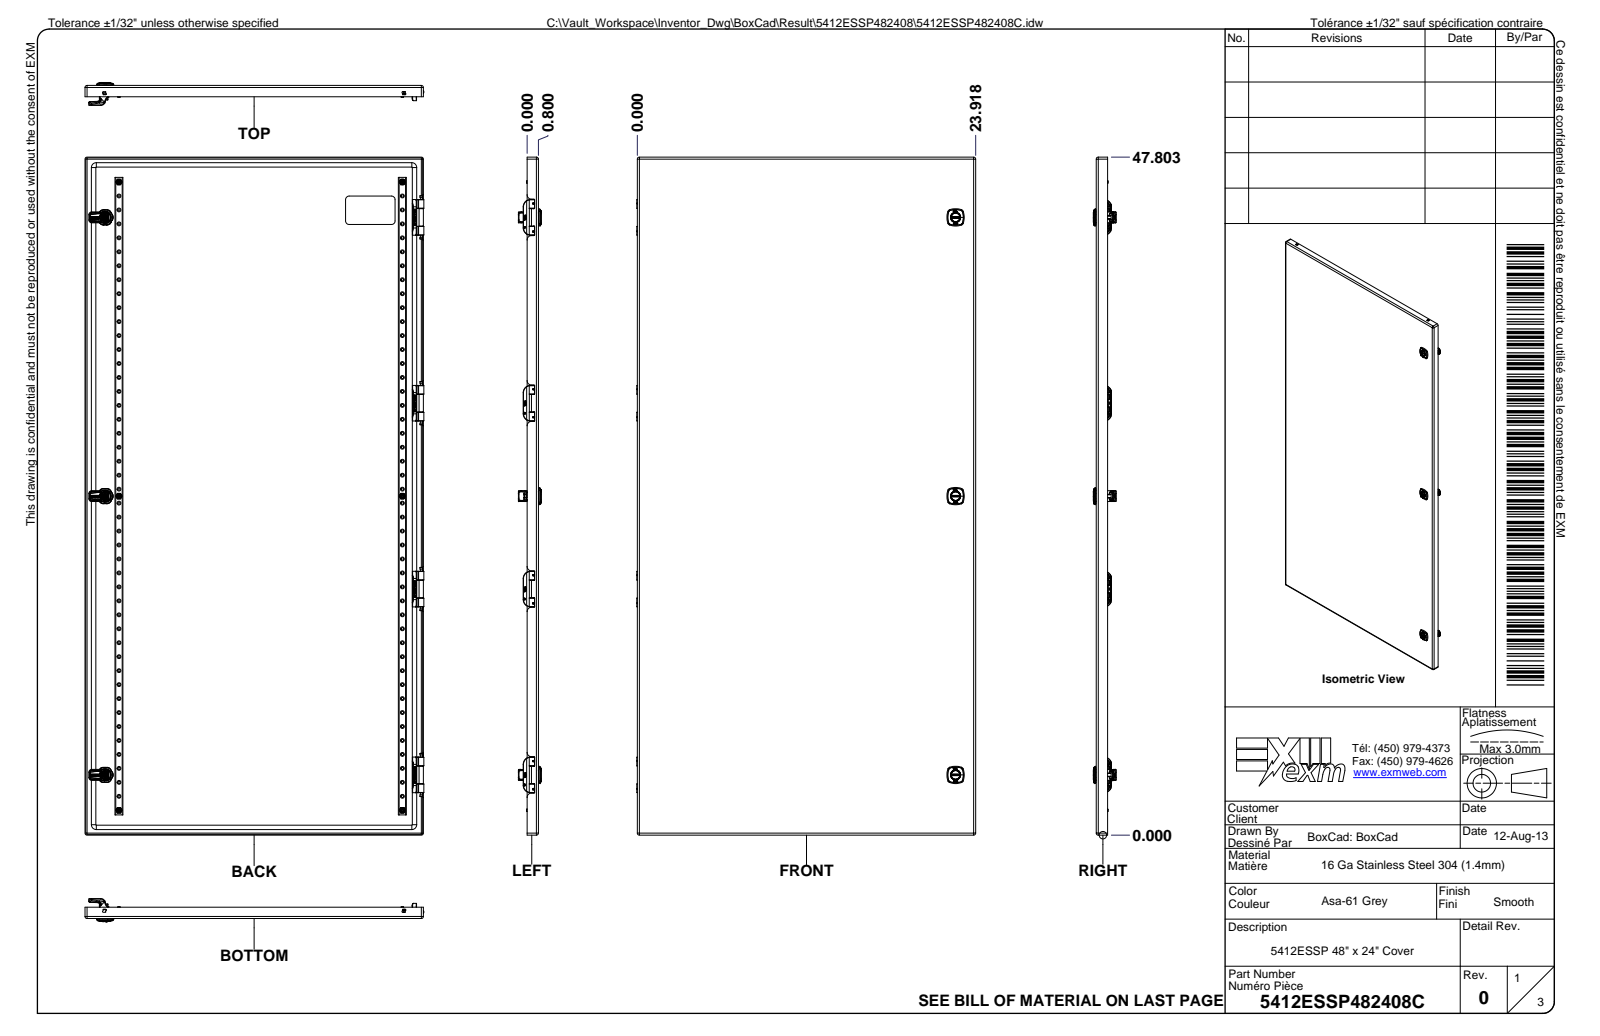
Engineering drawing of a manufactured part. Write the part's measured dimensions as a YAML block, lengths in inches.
part_name: "5412ESSP482408; 5412ESSP482408B; 5412ESSP482408B-P; STK-Q-16020 (+8 more)"
step_written_by: "Autodesk Inventor 2024 (AUTOMOTIVE_DESIGN)"
units: inches
bodies: {solids: 100, faces: 14637, planar: 4801, cylindrical: 3054, other: 6782}
overall_size: [48, 24, 9.306]
volume: 335.8
surface_area: 10384
round_holes:
  - {diameter: 0.165, count: 88}
  - {diameter: 0.03, count: 13}
  - {diameter: 0.201, count: 13}
  - {diameter: 0.315, count: 12}
  - {diameter: 0.311, count: 9}
  - {diameter: 0.044, count: 8}
  - {diameter: 0.29, count: 8}
  - {diameter: 0.197, count: 6}
  - {diameter: 0.268, count: 6}
  - {diameter: 0.27, count: 6}
  - {diameter: 0.236, count: 4}
  - {diameter: 0.354, count: 4}
round_bosses_or_shafts:
  - {diameter: 0.237, count: 88}
  - {diameter: 0.039, count: 16}
  - {diameter: 0.232, count: 14}
  - {diameter: 0.03, count: 13}
  - {diameter: 0.717, count: 6}
  - {diameter: 0.374, count: 6}
  - {diameter: 0.311, count: 6}
  - {diameter: 0.262, count: 6}
partial_cylinders:
  - {radius: 0.02, count: 156}
  - {radius: 0.008, count: 118}
  - {radius: 0.039, count: 96}
  - {radius: 0.012, count: 50}
  - {radius: 0.01, count: 40}
  - {radius: 0.031, count: 34}
  - {radius: 0.01, count: 24}
  - {radius: 0.059, count: 24}
face_to_face_distances: [0.053, 9.082, 9.029, 9.135, 0.927, 0.874, 8.155, 8.208, 0.105, 1.032]
hole_center_spacings: [1.969, 0.984, 2.953, 3.937, 4.921, 5.906, 6.89, 7.874]
